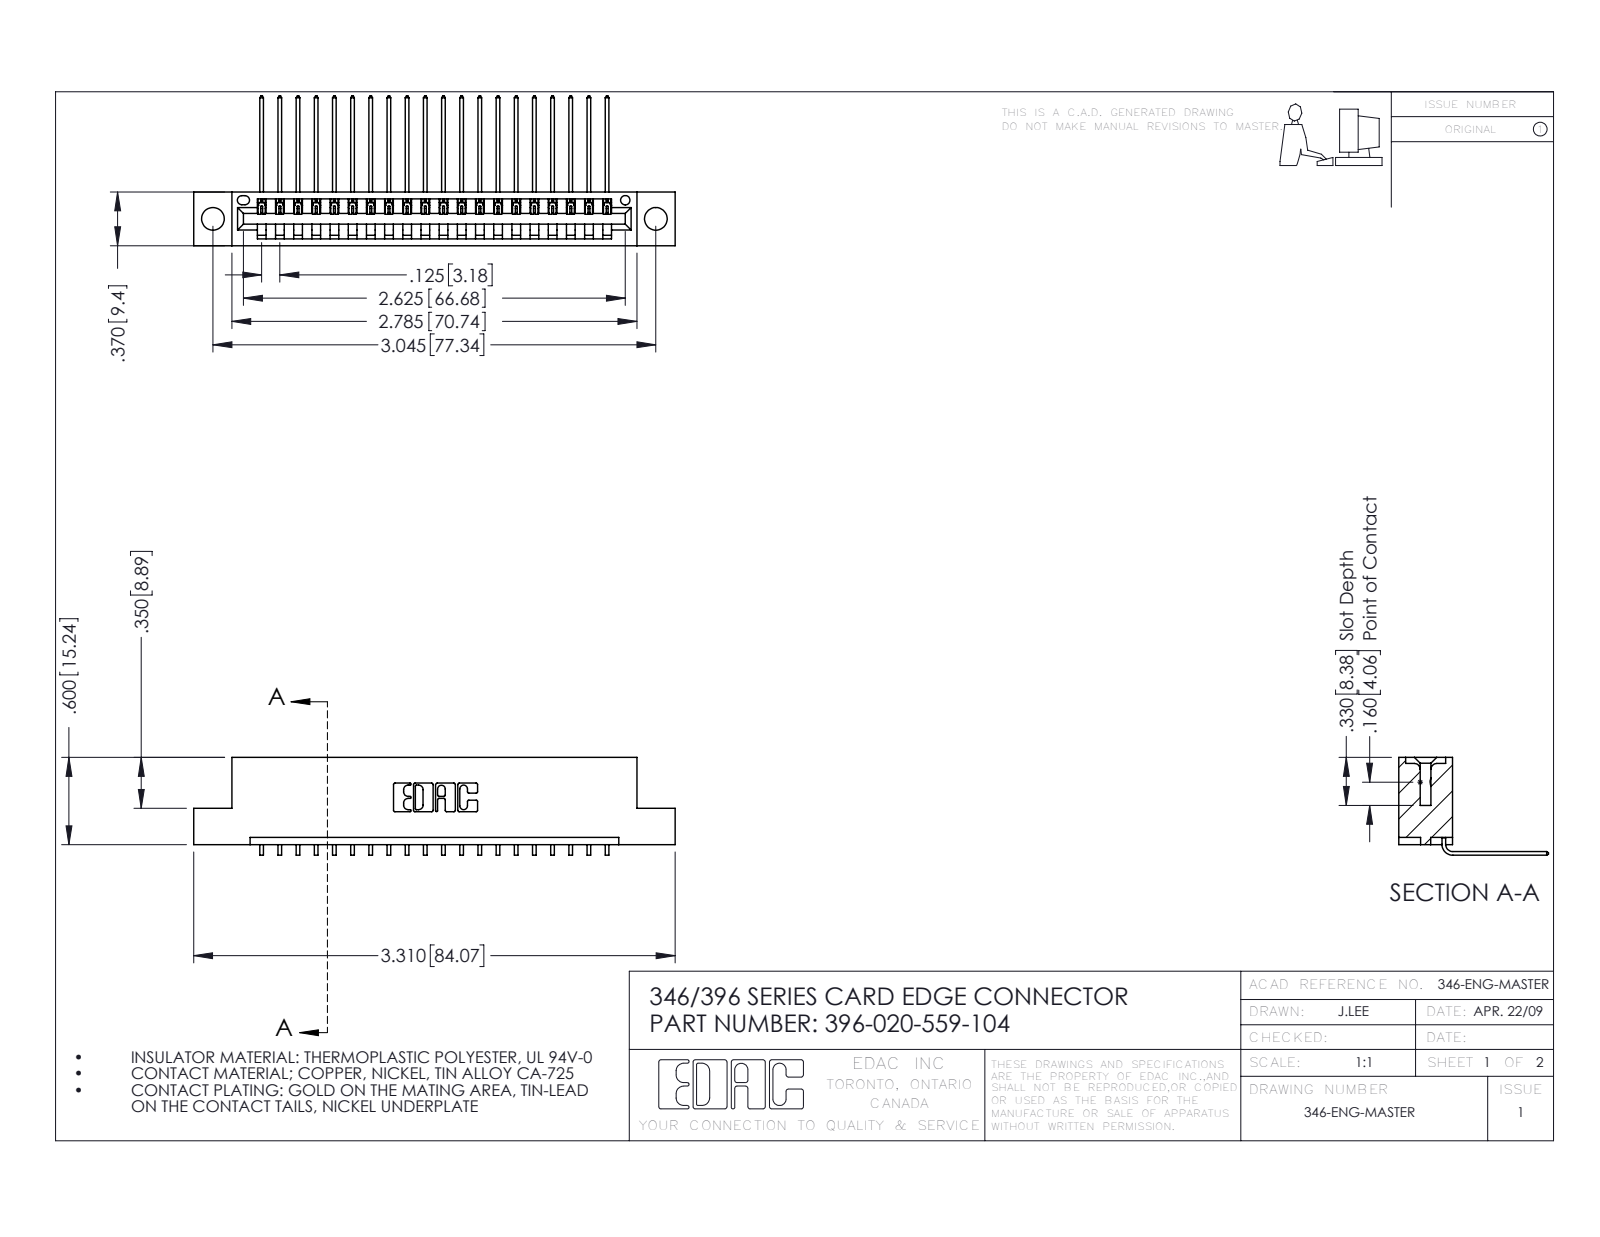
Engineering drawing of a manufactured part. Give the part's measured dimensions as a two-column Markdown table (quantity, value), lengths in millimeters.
| quantity | value |
| --- | --- |
| part name | 396-020-559-104; 345-292-001_558 559 Tail - 1; 346 Part_Flush Mounting Lugs - 0.156 Dia-TH |
| STEP written by | SolidWorks 2016 (CONFIG_CONTROL_DESIGN) |
| units | millimeters |
| bodies | 21 solids, 1322 faces (916 planar, 406 cylindrical, 0 other) |
| overall size | 84.1 × 26.2 × 17.1 |
| volume | 7 880 mm³ |
| surface area | 9 806 mm² |
| round holes (diameter × count) | 4 × 2, 1.6 × 1 |
| partial cylindrical surfaces (radius × count) | 0.2 × 40, 0.3 × 22, 0.2 × 6, 0.8 × 6, 0.7 × 3, 0.8 × 2, 1 × 2, 0.4 × 1 |
| main face-to-face distances | 1.2, 8.2, 9.4, 6.4, 1.8, 0.6, 7.6, 3.8, 5.6, 2.5 |
| hole center spacings | 6.2, 72.1, 77.3 |
